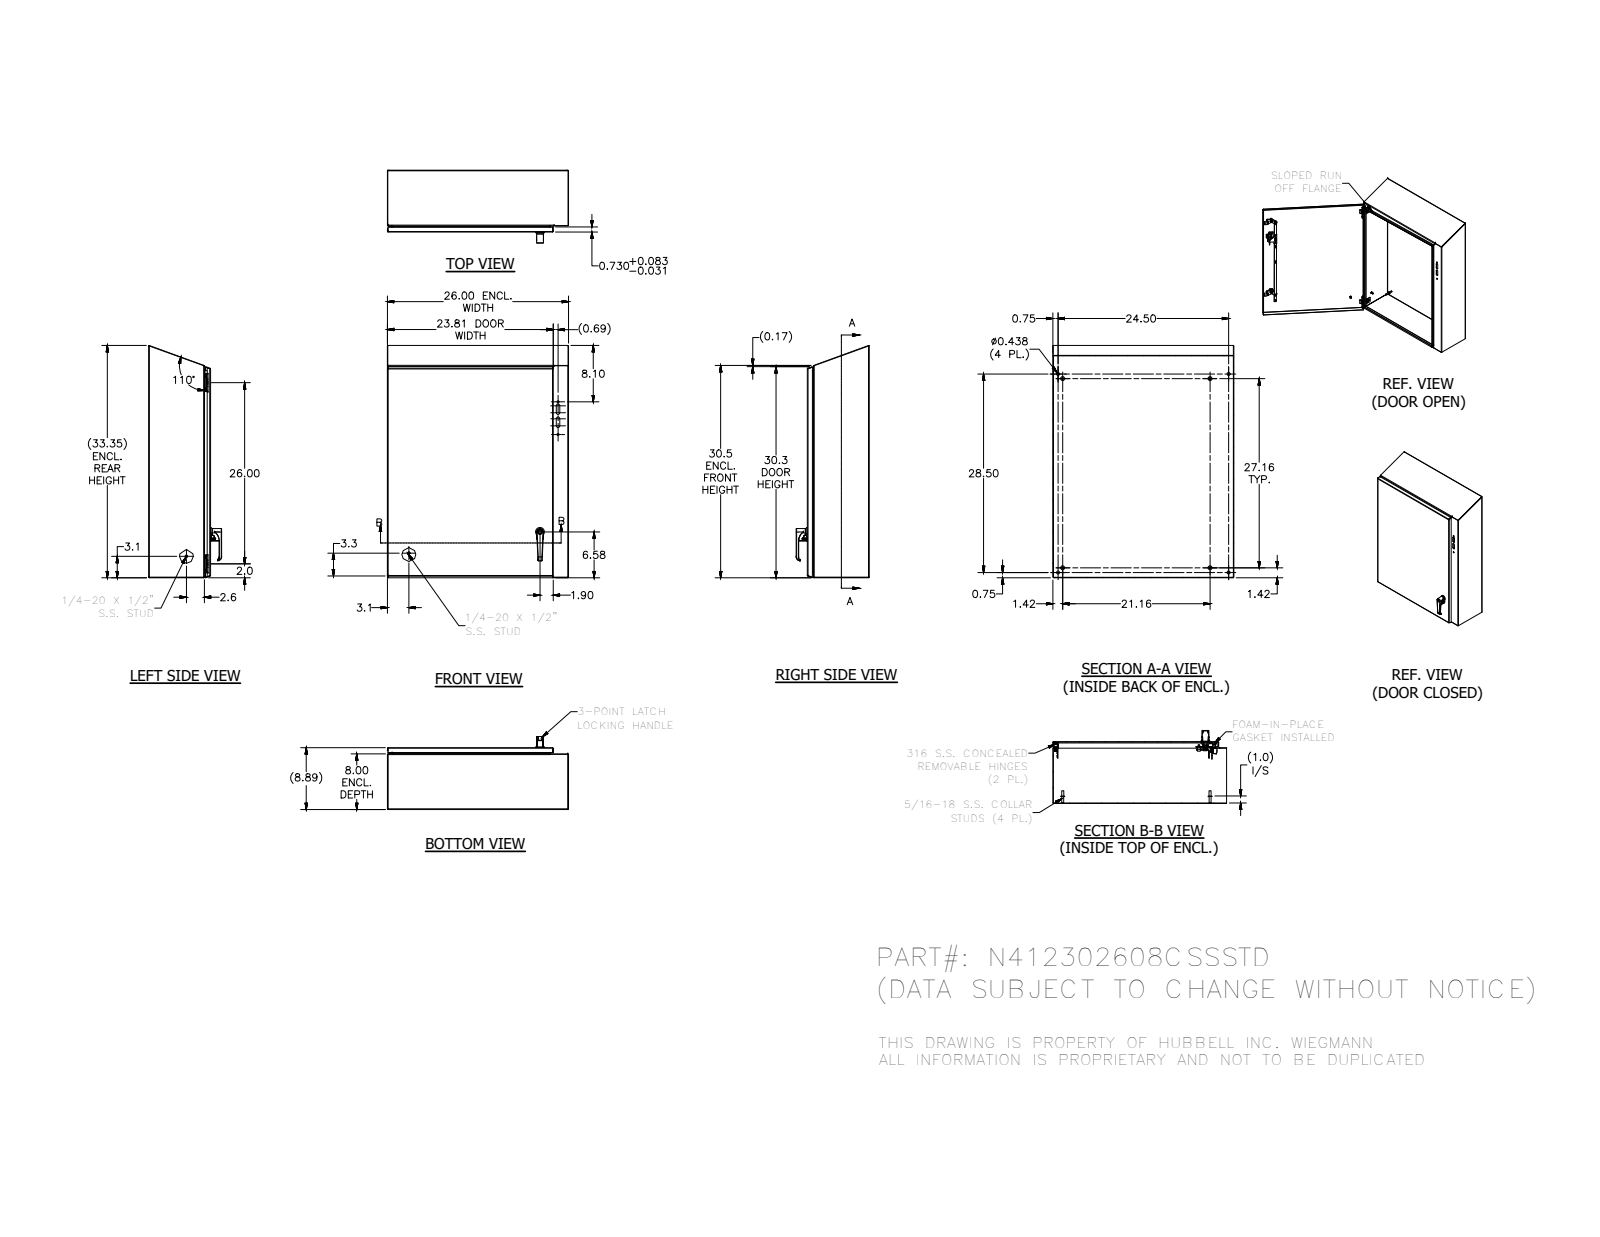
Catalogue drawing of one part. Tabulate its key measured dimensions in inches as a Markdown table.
| quantity | value |
| --- | --- |
| part name | N412302608CSSSTDB3S; 388151; N4122608CSSSTDTOP; 38846 (+8 more) |
| STEP written by | Autodesk Inventor 2016 (AUTOMOTIVE_DESIGN) |
| units | inches |
| bodies | 46 solids, 1852 faces (711 planar, 659 cylindrical, 482 other) |
| overall size | 33.348 × 26 × 10.481 |
| volume | 206 in³ |
| surface area | 5 679 in² |
| round holes (diameter × count) | 0.156 × 5, 0.093 × 4, 0.152 × 4, 0.167 × 4, 0.172 × 4, 0.187 × 4, 0.437 × 4, 0.281 × 2, 0.102 × 1, 0.187 × 1, 0.197 × 1, 0.201 × 1 |
| round bosses / shafts (diameter × count) | 0.25 × 12, 0.563 × 4, 0.36 × 4, 0.32 × 4, 0.3 × 4, 0.275 × 4, 0.256 × 4, 0.164 × 4 |
| partial cylindrical surfaces (radius × count) | 0.02 × 38, 0.012 × 30, 0.031 × 26, 0.05 × 26, 0.016 × 18, 0.125 × 17, 0.105 × 16, 0.032 × 8 |
| main face-to-face distances | 0.074, 8.813, 8.739, 8.887, 25.926, 26, 25.852, 0.059, 7.926, 0.887 |
| hole center spacings | 26, 24.9, 0.5, 0.656, 0.66, 0.984, 1.307, 1.311 |
